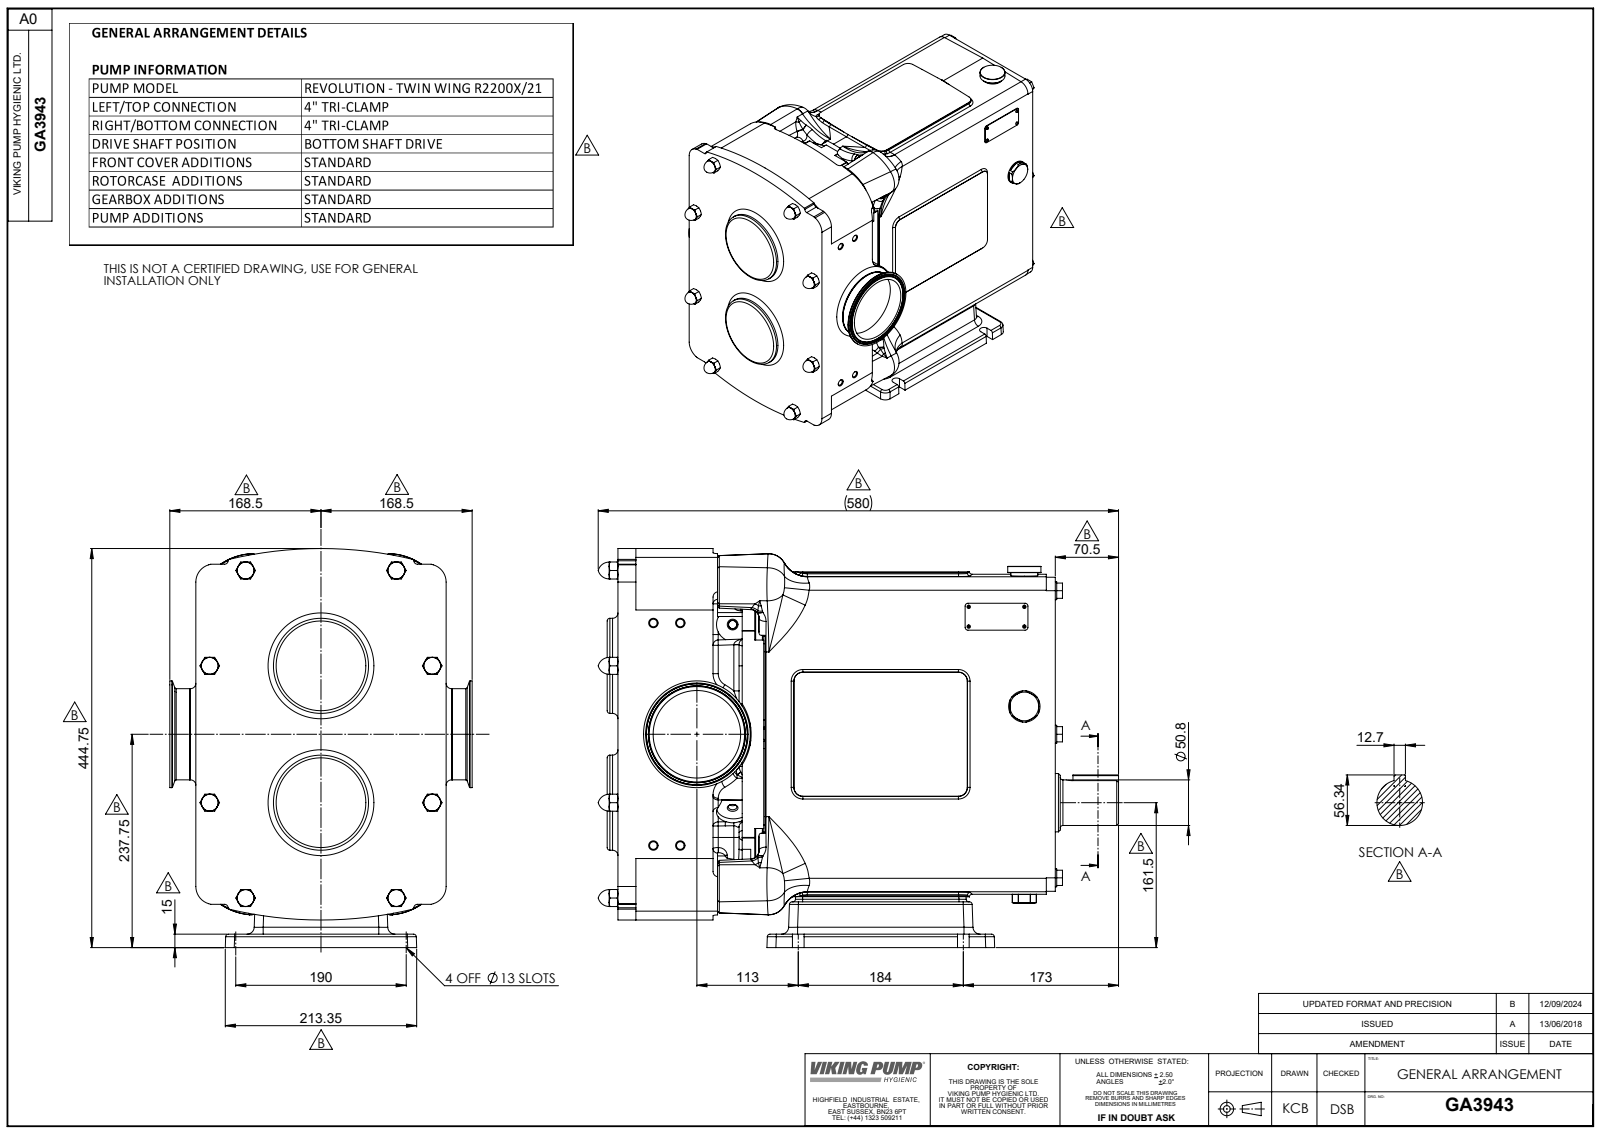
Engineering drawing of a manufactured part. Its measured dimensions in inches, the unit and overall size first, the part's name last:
Units: inches
Overall size (bounding box): 22.835 × 17.51 × 13.268
Round holes (diameter × count): ⌀0.335 ×4, ⌀5.866 ×2, ⌀1.378 ×1, ⌀3.841 ×1
Round bosses / shafts (diameter × count): ⌀0.551 ×10, ⌀0.315 ×10, ⌀0.787 ×6, ⌀0.709 ×4, ⌀7.362 ×2, ⌀5.512 ×2, ⌀4.173 ×2, ⌀1.24 ×2
Partial cylindrical surfaces — rounded edges, fillets, slot ends (radius × count): R0.236 ×48, R0.118 ×44, R0.394 ×28, R0.008 ×24, R0.039 ×16, R0.197 ×16, R0.315 ×10, R0.591 ×8
Main face-to-face distances: 7.48, 19.193, 0.118, 7.598, 13.74, 5.453, 1.634, 9.35, 1.752, 9.232
Hole centre spacings: 1.181, 4.936, 5.242, 9.764, 9.835, 6.004
Volume: 2 387 in³ · Surface area: 1 927 in²
Bodies: 4 solids, 1647 faces (497 planar, 405 cylindrical, 745 other)
Part name (STEP PRODUCT): RA94-5121-66M; GA3943; R2200 CPP H BSD
STEP written by: SolidWorks 2023 (AUTOMOTIVE_DESIGN)
